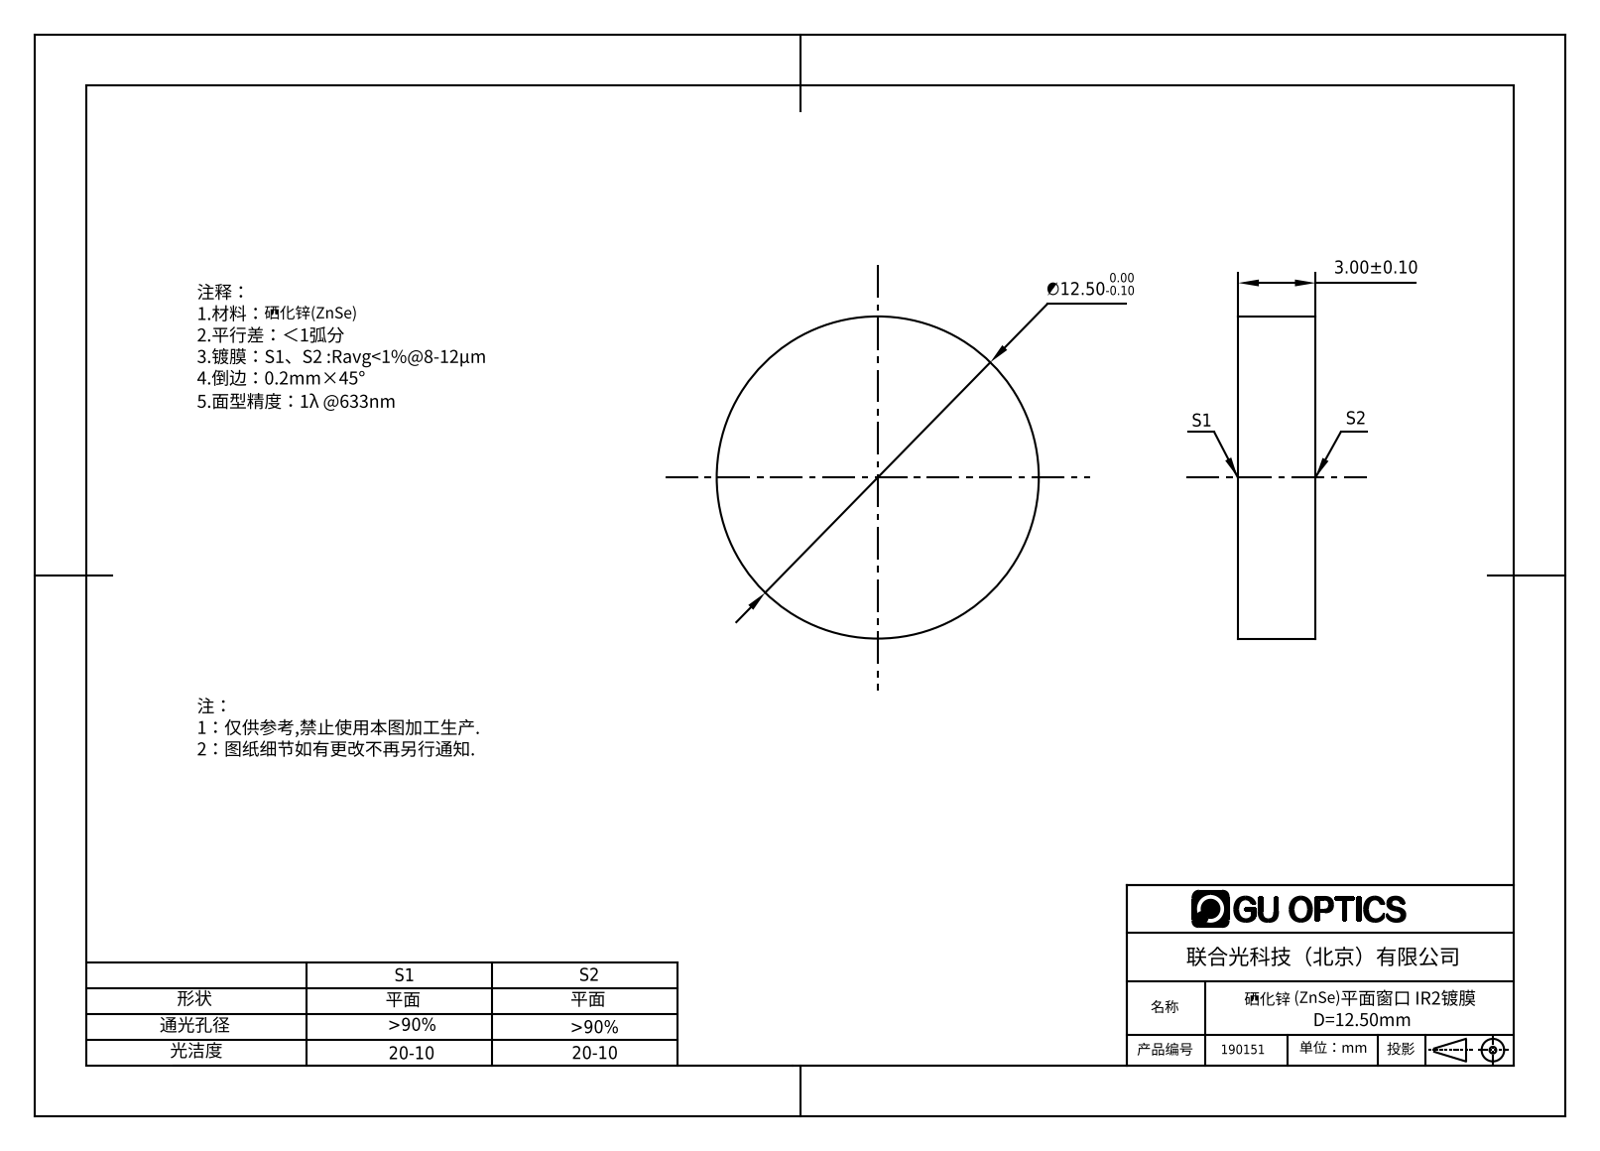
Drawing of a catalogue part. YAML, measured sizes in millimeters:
part_name: "190150"
step_written_by: "SolidWorks 2016 (AUTOMOTIVE_DESIGN)"
units: millimeters
bodies: {solids: 1, faces: 4, planar: 2, cylindrical: 2, other: 0}
overall_size: [12.5, 12.5, 3]
volume: 368
surface_area: 363
round_bosses_or_shafts:
  - {diameter: 12.5, count: 1}
face_to_face_distances: [3]
